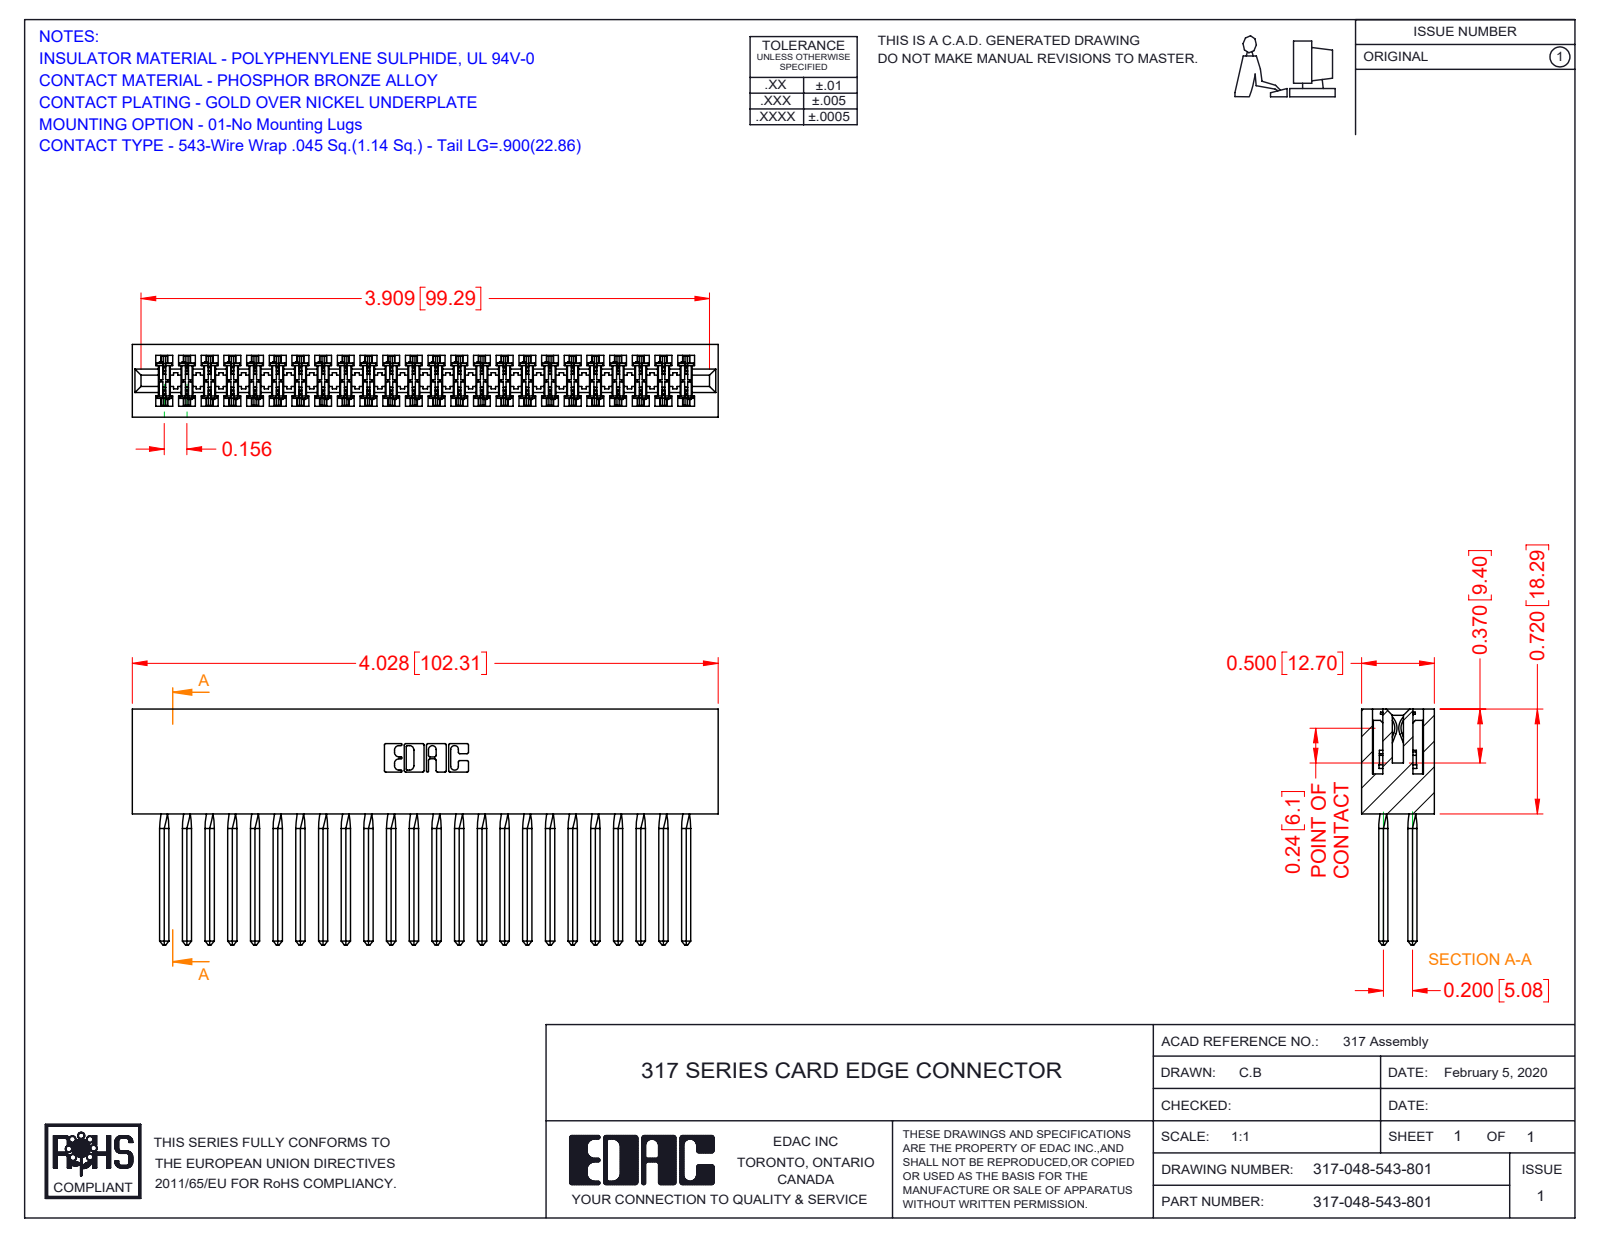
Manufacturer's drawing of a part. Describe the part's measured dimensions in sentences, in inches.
The part is named "317 Part_Lugless; 317-048-543-801; 317-290-001_543". Its 3-D file was written by "SolidWorks 2016 (CONFIG_CONTROL_DESIGN)". It is 49 solids with 4362 faces: 3554 planar, 616 cylindrical and 192 other. Overall it measures 4.028 by 1.62 by 0.5 inches. Its volume is 1.135 cubic inches and its surface area 43.06 square inches. Partial cylindrical surfaces (rounded edges, fillets, slot ends): 96 of radius 0.015, 22 of radius 0.01, 6 of radius 0.007, 6 of radius 0.031, 3 of radius 0.026, 2 of radius 0.095, 2 of radius 0.1, 2 of radius 0.11. The main face-to-face distances are 0.075, 0.5, 0.425, 0.11, 0.35, 0.195, 0.116, 0.22, 0.094, 0.72.
